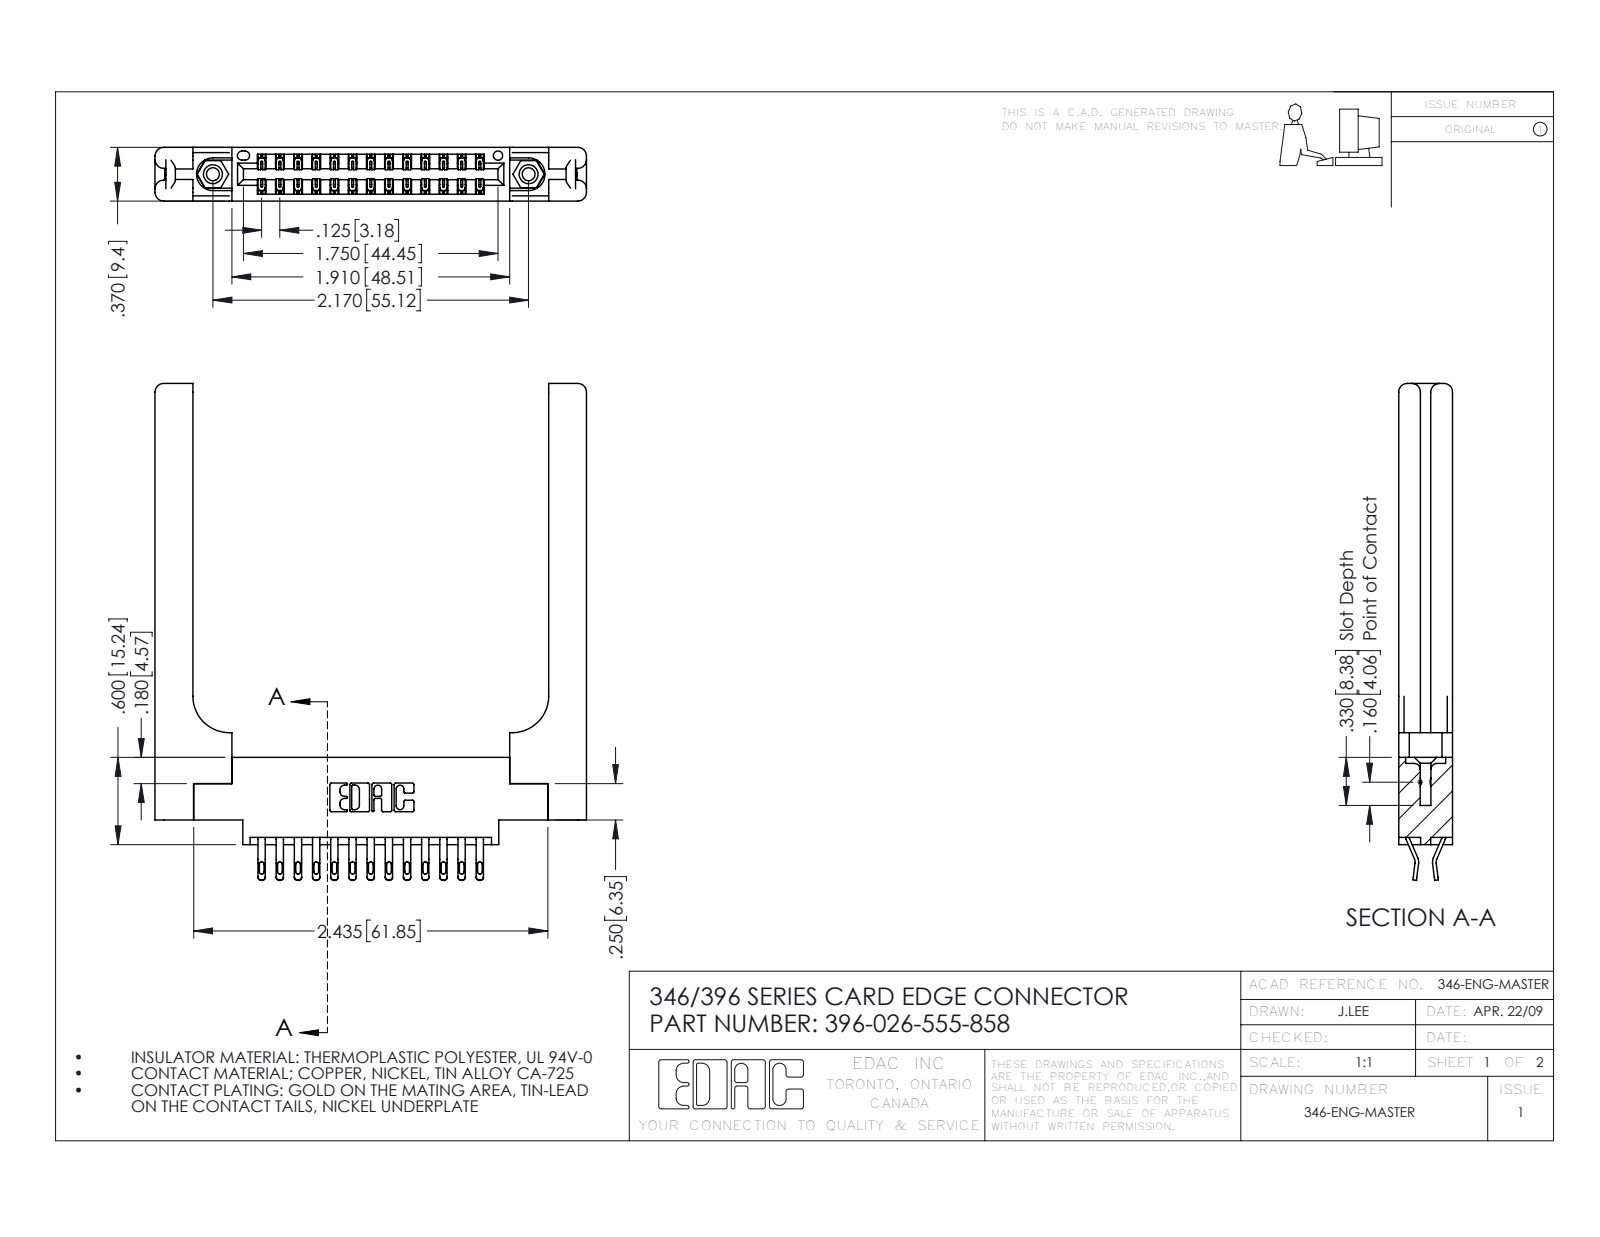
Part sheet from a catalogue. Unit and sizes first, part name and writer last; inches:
Units: inches
Overall size (bounding box): 3.415 × 2.966 × 0.37
Round holes (diameter × count): ⌀0.089 ×2, ⌀0.125 ×2, ⌀0.156 ×2, ⌀0.064 ×1
Round bosses / shafts (diameter × count): ⌀0.155 ×2
Partial cylindrical surfaces — rounded edges, fillets, slot ends (radius × count): R0.016 ×52, R0.02 ×52, R0.006 ×39, R0.01 ×22, R0.06 ×16, R0.007 ×6, R0.031 ×6, R0.026 ×3
Main face-to-face distances: 0.37, 0.15, 0.072, 0.148, 0.048, 0.322, 0.102, 0.22, 0.173, 0.25
Hole centre spacings: 0.246, 1.964, 2.17
Volume: 0.887 in³ · Surface area: 22.7 in²
Bodies: 31 solids, 1890 faces (1086 planar, 744 cylindrical, 60 other)
Part name (STEP PRODUCT): 346-220-058_345-220-058; 346 Part_0.170 Offset - 0.156 Dia-TH; 345-292-001_555 Tail; 396-026-555-858 (+1 more)
STEP written by: SolidWorks 2016 (CONFIG_CONTROL_DESIGN)
